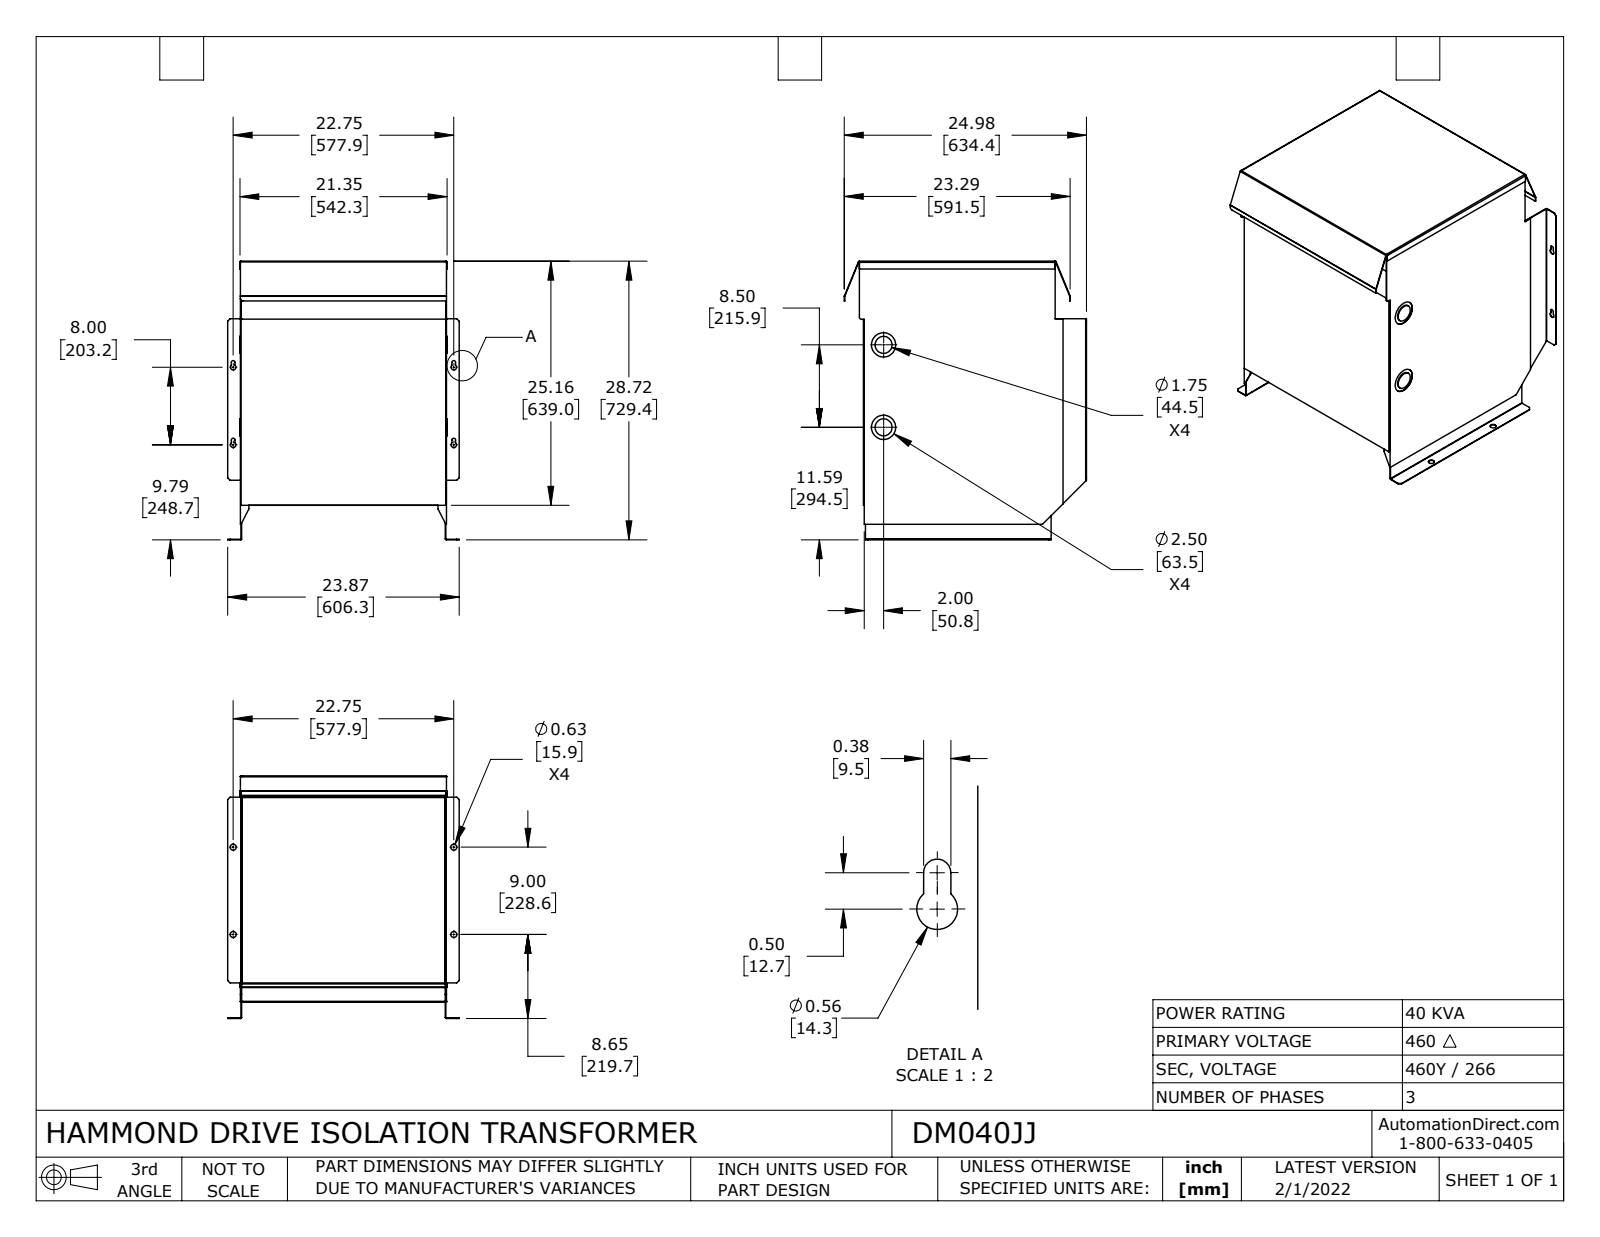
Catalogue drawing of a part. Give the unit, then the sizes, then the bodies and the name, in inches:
Units: inches
Overall size (bounding box): 28.718 × 24.978 × 23.87
Round holes (diameter × count): ⌀0.625 ×4, ⌀2.5 ×2, ⌀0.281 ×1
Round bosses / shafts (diameter × count): ⌀1.75 ×2
Partial cylindrical surfaces — rounded edges, fillets, slot ends (radius × count): R0.03 ×12, R0.09 ×12, R0.06 ×6, R0.11 ×6, R0.188 ×4, R0.281 ×4, R0.25 ×2
Main face-to-face distances: 0.06, 0.05, 0.06, 21.19, 21.13, 21.19, 21.25, 19.387, 19.437, 19.328
Hole centre spacings: 9, 22.75, 24.465, 6.083, 8.5, 14.534
Volume: 205 in³ · Surface area: 7 249 in²
Bodies: 5 solids, 236 faces (152 planar, 82 cylindrical, 2 other)
Part name (STEP PRODUCT): DM040JJ
STEP written by: SolidWorks 2021 (CONFIG_CONTROL_DESIGN)
